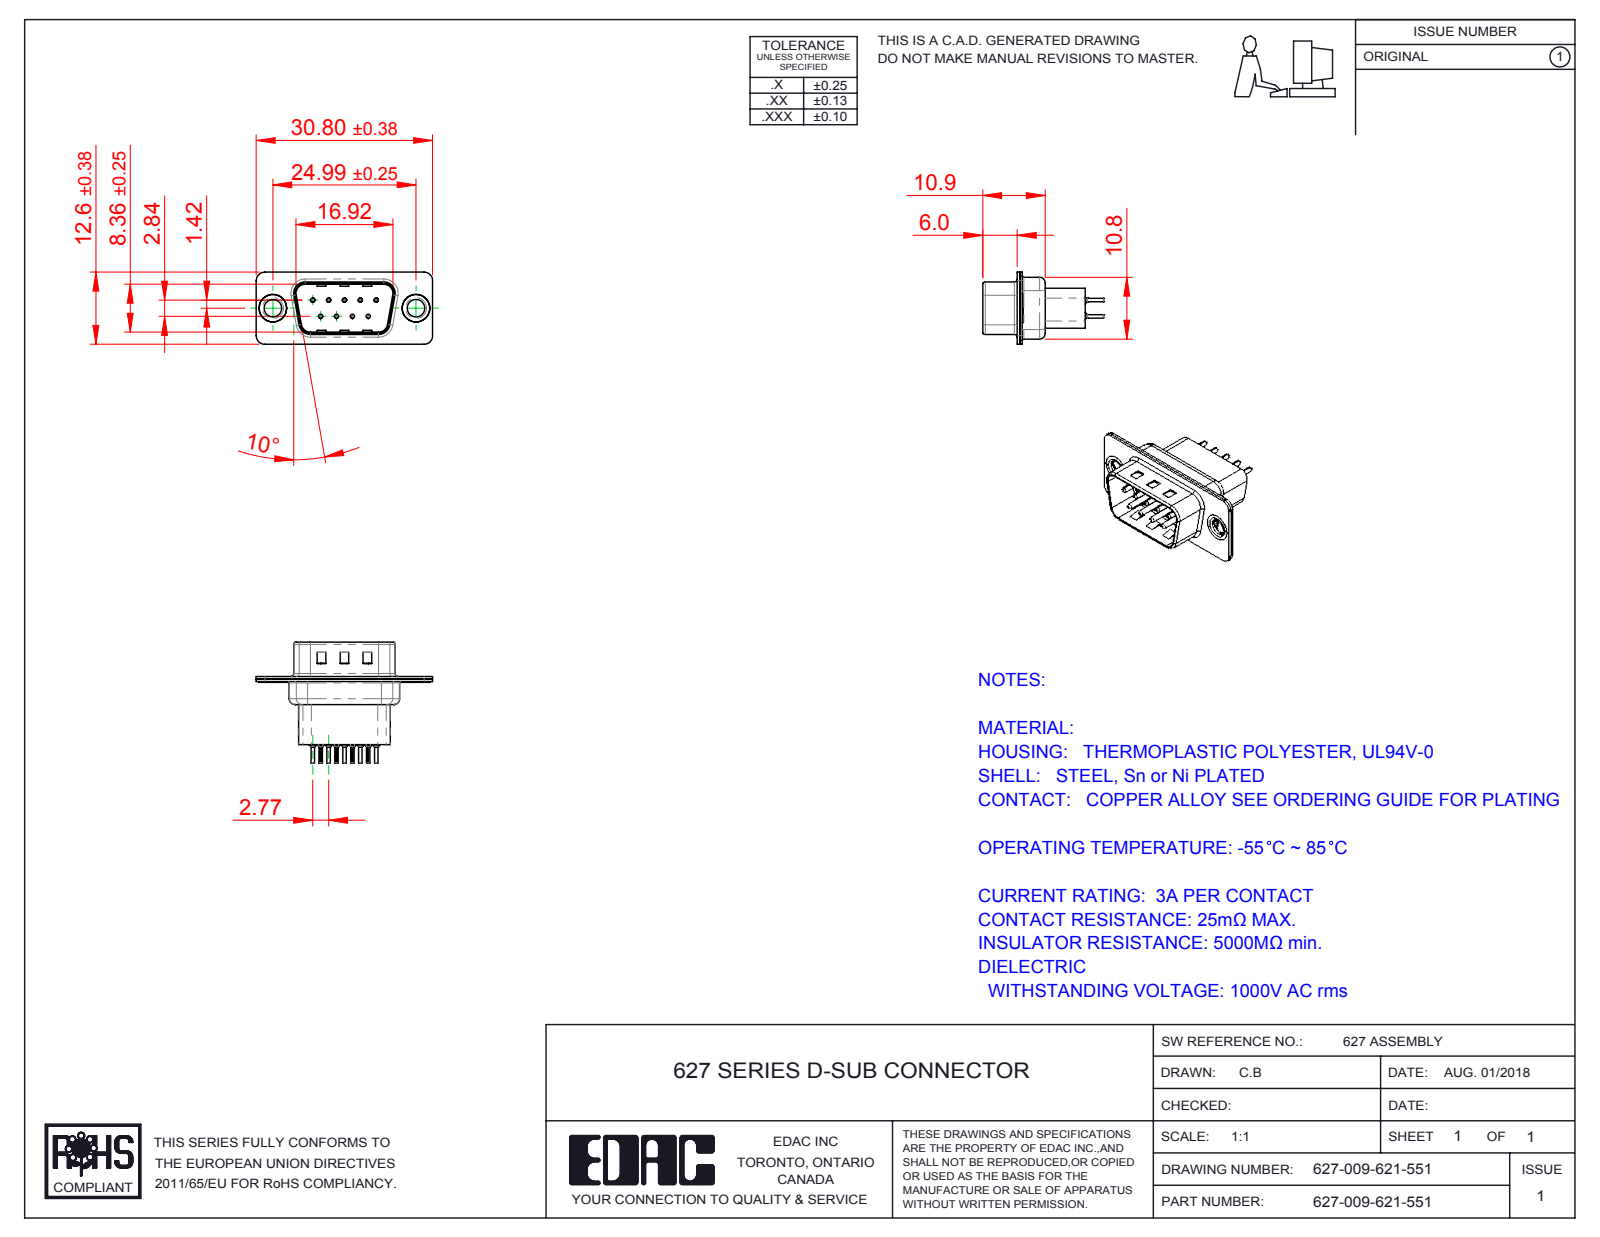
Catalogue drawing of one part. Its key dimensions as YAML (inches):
part_name: "627 Shell Front_09 Contacts; 627 Housing_09 HP; 627 Contact Row 2_21H; 627 Shell Rear_09 Contacts (+3 more)"
step_written_by: "SolidWorks 2016 (CONFIG_CONTROL_DESIGN)"
units: inches
bodies: {solids: 14, faces: 1160, planar: 323, cylindrical: 446, other: 391}
overall_size: [1.213, 0.831, 0.496]
volume: 0.106
surface_area: 7.178
round_holes:
  - {diameter: 0.008, count: 9}
  - {diameter: 0.014, count: 9}
  - {diameter: 0.043, count: 9}
  - {diameter: 0.063, count: 9}
  - {diameter: 0.12, count: 2}
  - {diameter: 0.157, count: 2}
  - {diameter: 0.189, count: 2}
round_bosses_or_shafts:
  - {diameter: 0.079, count: 9}
  - {diameter: 0.059, count: 9}
  - {diameter: 0.03, count: 9}
  - {diameter: 0.024, count: 9}
  - {diameter: 0.197, count: 2}
  - {diameter: 0.193, count: 2}
  - {diameter: 0.14, count: 2}
partial_cylinders:
  - {radius: 0.004, count: 18}
  - {radius: 0.059, count: 18}
  - {radius: 0.079, count: 12}
  - {radius: 0.02, count: 8}
  - {radius: 0.063, count: 8}
  - {radius: 0.01, count: 4}
  - {radius: 0.024, count: 4}
  - {radius: 0.026, count: 4}
face_to_face_distances: [0.018, 0.016, 0.035, 0.032, 0.377, 0.055, 0.059, 0.027, 0.302, 0.043]
hole_center_spacings: [0.124, 0.109, 0.218, 0.198, 0.198, 0.327, 0.294, 0.295]
